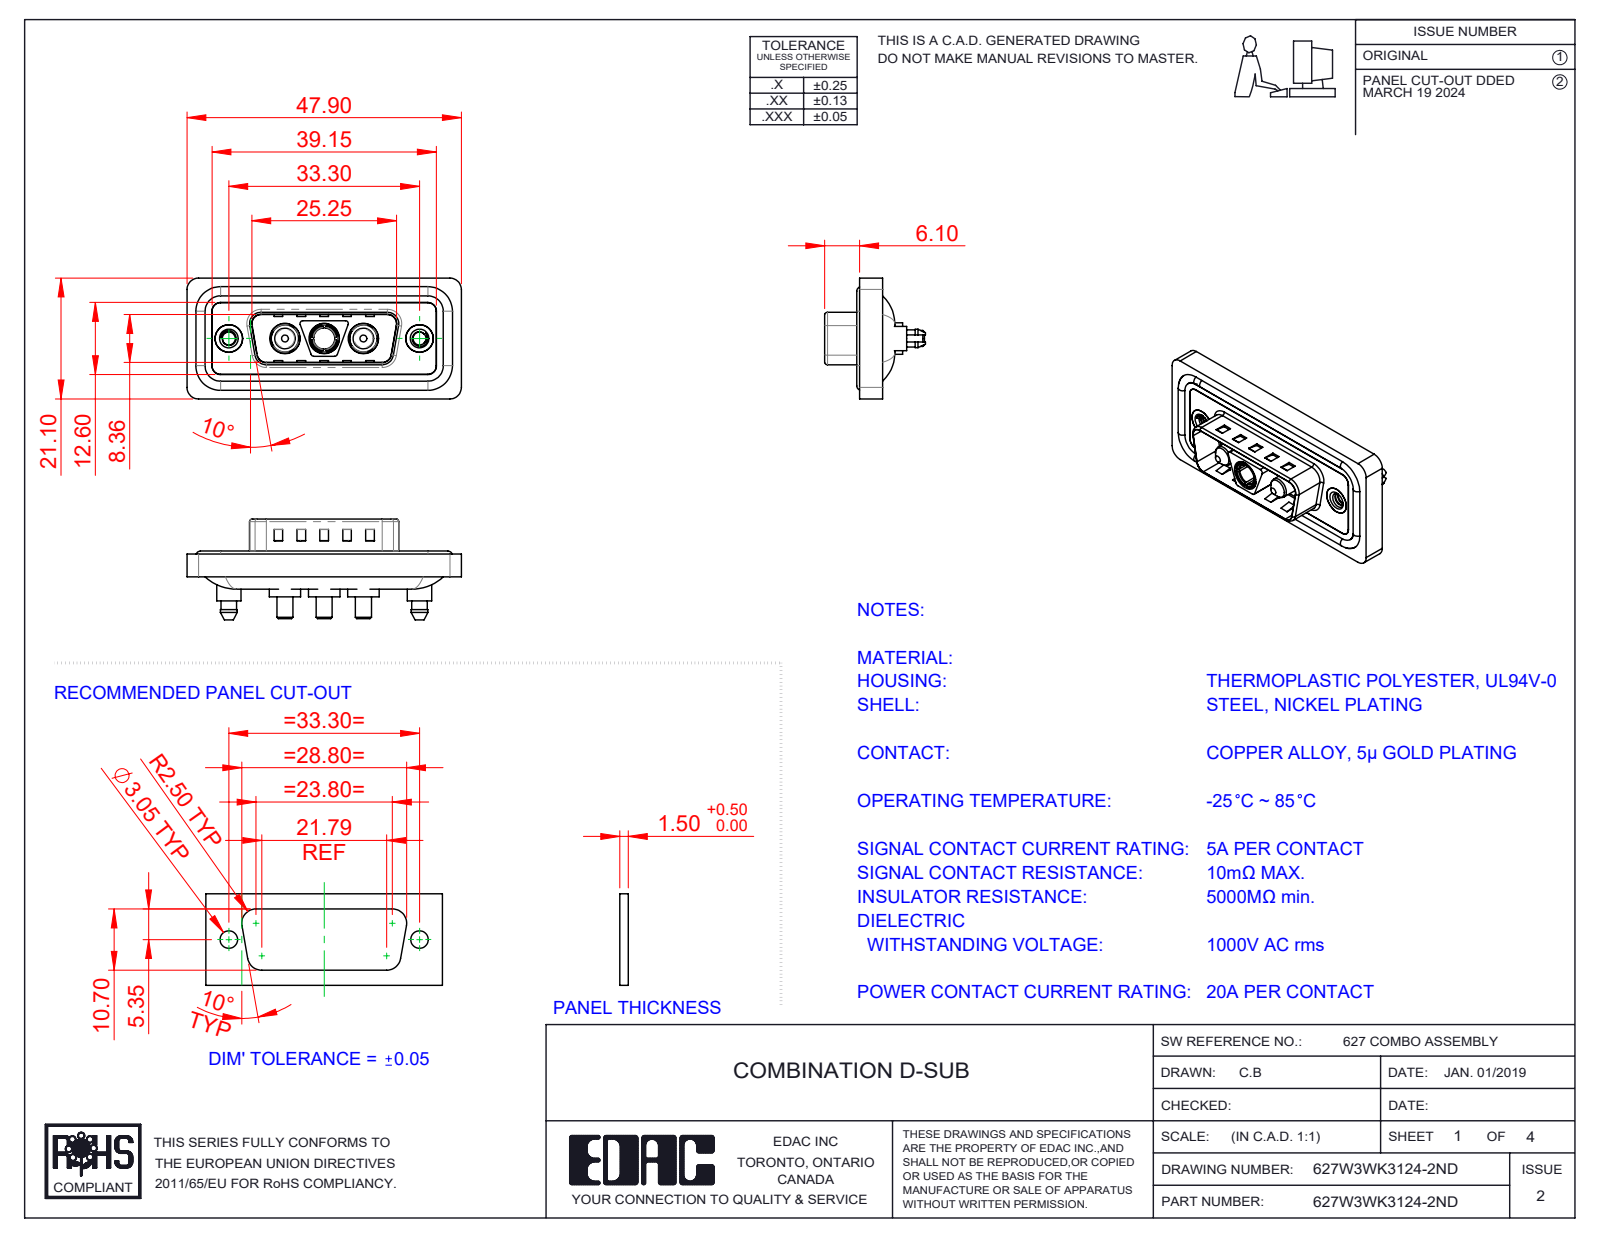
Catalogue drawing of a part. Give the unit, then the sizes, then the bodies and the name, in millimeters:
Units: millimetres
Overall size (bounding box): 47.9 × 21.1 × 17.6
Round holes (diameter × count): ⌀4.85 ×3, ⌀5.3 ×3, ⌀2.26 ×2, ⌀4 ×2, ⌀4.8 ×2, ⌀5 ×2, ⌀3.7 ×1
Round bosses / shafts (diameter × count): ⌀1.6 ×4, ⌀5.5 ×3, ⌀5.2 ×3, ⌀4.75 ×3, ⌀3.75 ×3, ⌀2.8 ×3, ⌀5.4 ×2, ⌀4.9 ×2
Partial cylindrical surfaces — rounded edges, fillets, slot ends (radius × count): R1.5 ×28, R2 ×20, R0.5 ×12, R1.6 ×10, R0.25 ×4, R0.6 ×4, R0.65 ×4, R0.9 ×4
Main face-to-face distances: 0.4, 1.1, 1.5, 0.5, 1.6, 3.1, 2.9, 4, 0.7, 0.82
Hole centre spacings: 6.85, 9.8, 16.65, 23.5, 13.7, 33.3
Volume: 5 823 mm³ · Surface area: 9 463 mm²
Bodies: 13 solids, 667 faces (247 planar, 290 cylindrical, 130 other)
Part name (STEP PRODUCT): 627Combo Shell Front_15 Contacts; 627Combo Threaded Boardlock_5; 627Combo Threaded Boardlock_D; 627Combo Waterproof Housing_15 Contacts (+5 more)
STEP written by: SolidWorks 2023 (CONFIG_CONTROL_DESIGN)
